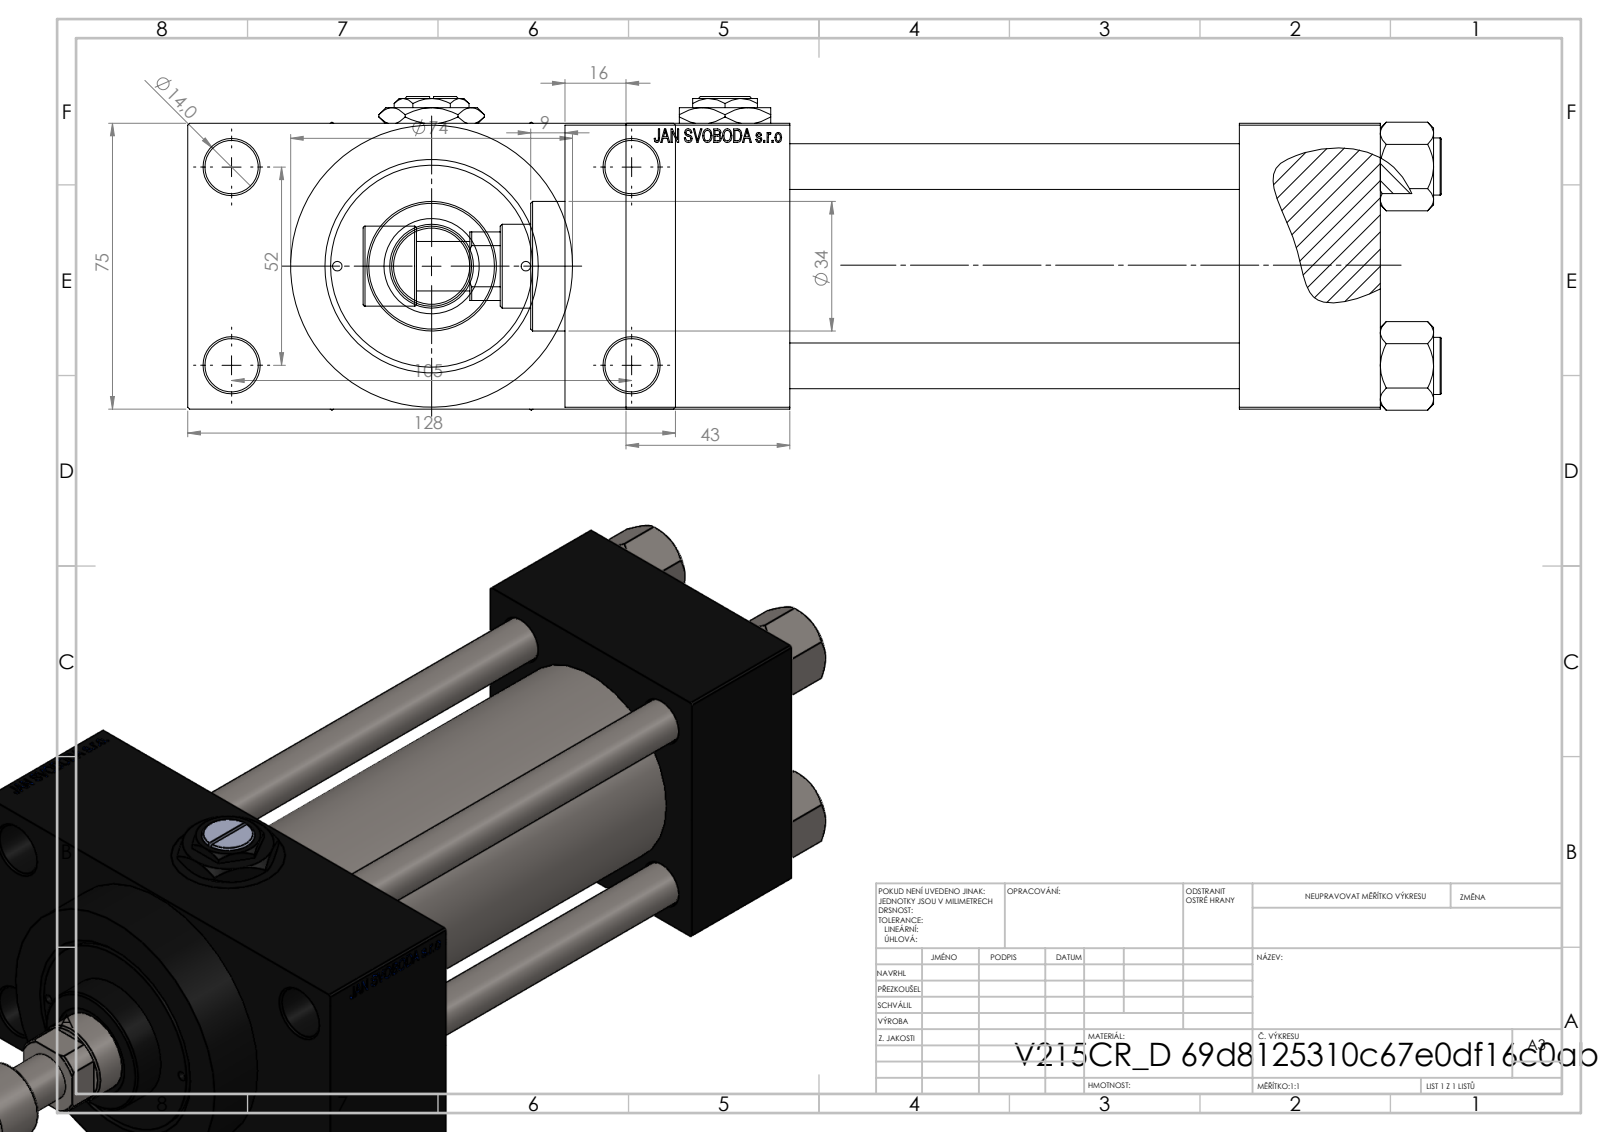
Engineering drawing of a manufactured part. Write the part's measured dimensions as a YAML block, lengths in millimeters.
part_name: "Zatka_pro_OIL_PORT; V215CR_VCP_D; V215CR_D_TYCINKA; V215CR_ROD_END_F (+3 more)"
step_written_by: "SolidWorks 2019 (CONFIG_CONTROL_DESIGN)"
units: millimeters
bodies: {solids: 13, faces: 1170, planar: 526, cylindrical: 100, other: 544}
overall_size: [283, 128, 82.27]
volume: 881686
surface_area: 203584
round_holes:
  - {diameter: 12, count: 4}
  - {diameter: 14, count: 4}
  - {diameter: 20.96, count: 3}
  - {diameter: 30, count: 3}
  - {diameter: 2.5, count: 2}
  - {diameter: 7, count: 2}
  - {diameter: 10.5, count: 1}
  - {diameter: 22, count: 1}
  - {diameter: 25, count: 1}
  - {diameter: 41, count: 1}
  - {diameter: 50, count: 1}
  - {diameter: 53, count: 1}
round_bosses_or_shafts:
  - {diameter: 15, count: 4}
  - {diameter: 74, count: 1}
  - {diameter: 56, count: 1}
  - {diameter: 34, count: 1}
  - {diameter: 21, count: 1}
  - {diameter: 13, count: 1}
face_to_face_distances: [75, 118, 37, 155, 26.5, 198, 161, 43, 101.5, 16]
hole_center_spacings: [26.19, 26.35, 36.98, 38.03, 52.3, 57.22, 58.43, 58.59]
